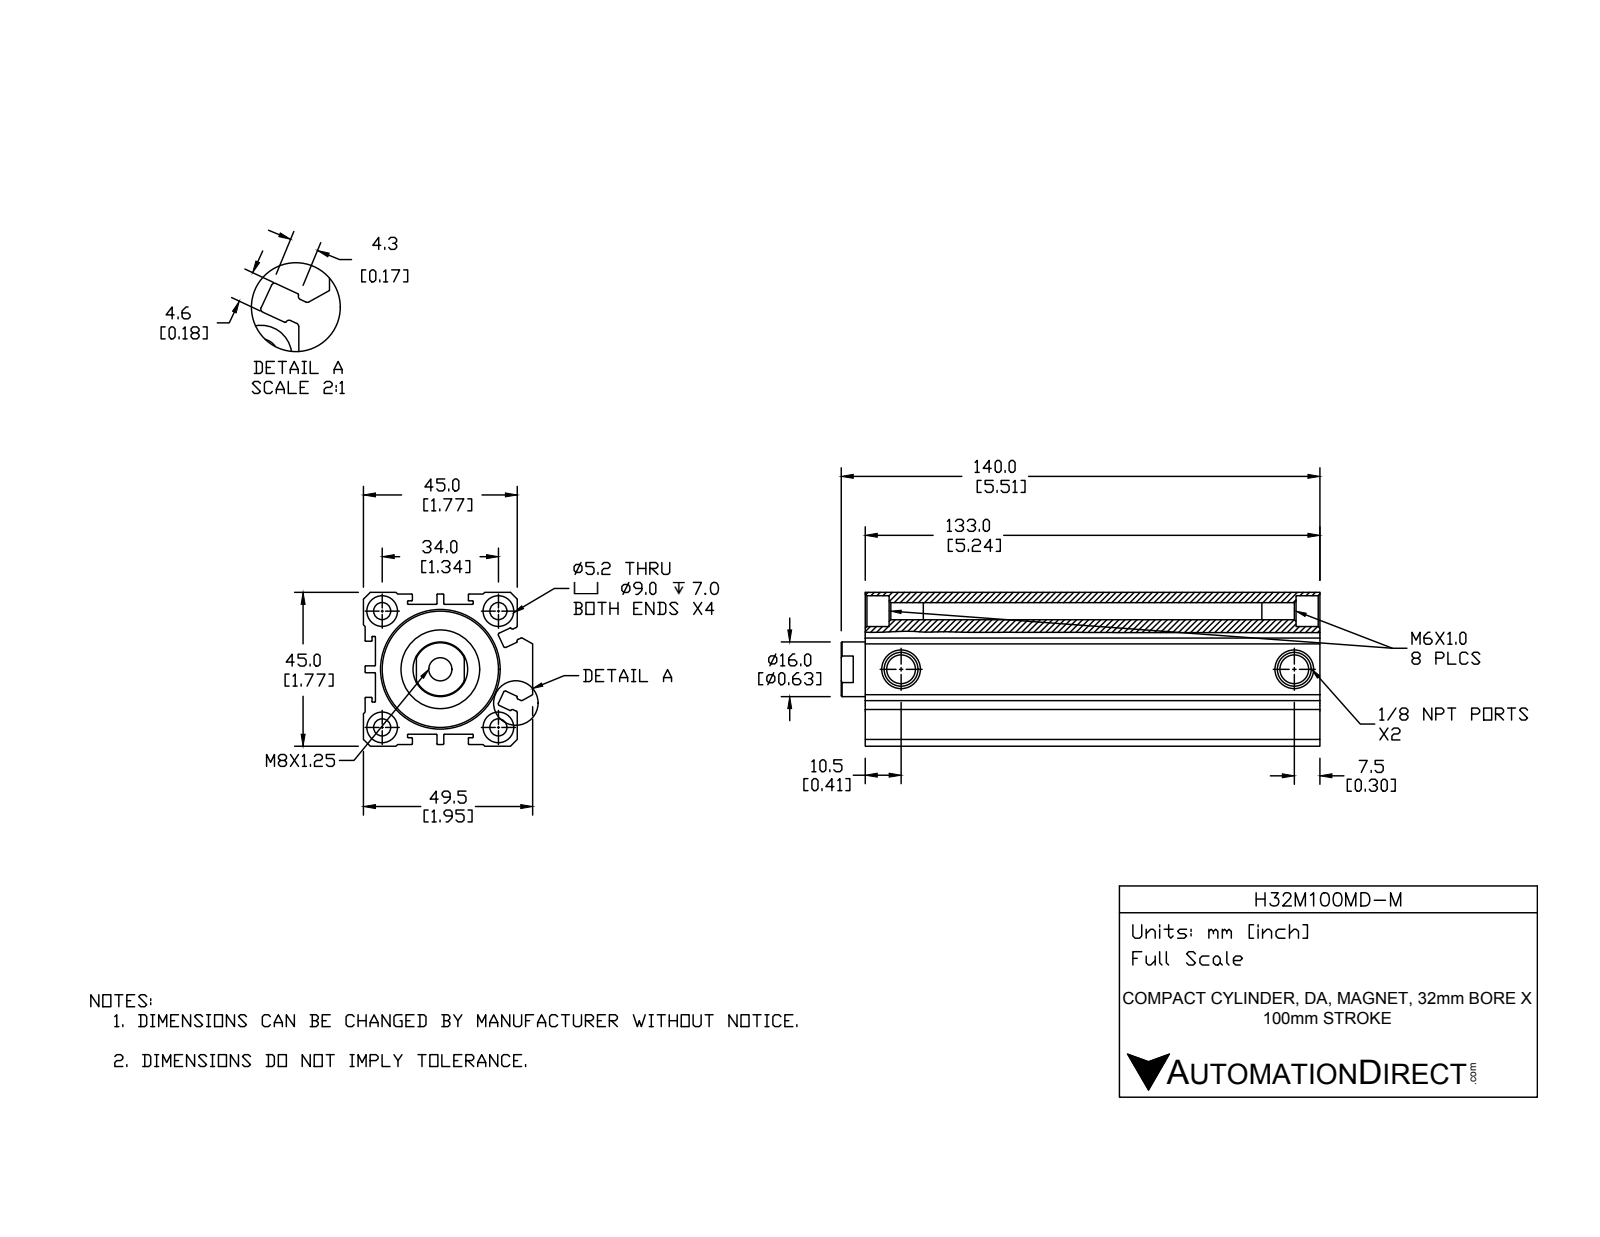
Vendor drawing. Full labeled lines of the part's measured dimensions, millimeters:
Part name (STEP PRODUCT): H32M100MD-M-BODY; H32M100MD-M; H32M100MD-M-PISTON
STEP written by: SolidWorks 2015 (CONFIG_CONTROL_DESIGN)
Units: millimetres
Bodies: 2 solids, 255 faces (99 planar, 103 cylindrical, 53 other)
Overall size (bounding box): 140 × 49.5 × 45
Volume: 171 923 mm³ · Surface area: 71 056 mm²
Round holes (diameter × count): ⌀5 ×4, ⌀9 ×4, ⌀8.43 ×2, ⌀6.8 ×1, ⌀16 ×1, ⌀23 ×1, ⌀28 ×1, ⌀32 ×1, ⌀34 ×1
Round bosses / shafts (diameter × count): ⌀20 ×1
Partial cylindrical surfaces — rounded edges, fillets, slot ends (radius × count): R0.2 ×40, R0.5 ×12
Main face-to-face distances: 3.5, 41.5, 3, 45, 0.5, 44.5, 4.5, 41, 38, 21
Hole centre spacings: 24.04, 34, 48.08, 115
